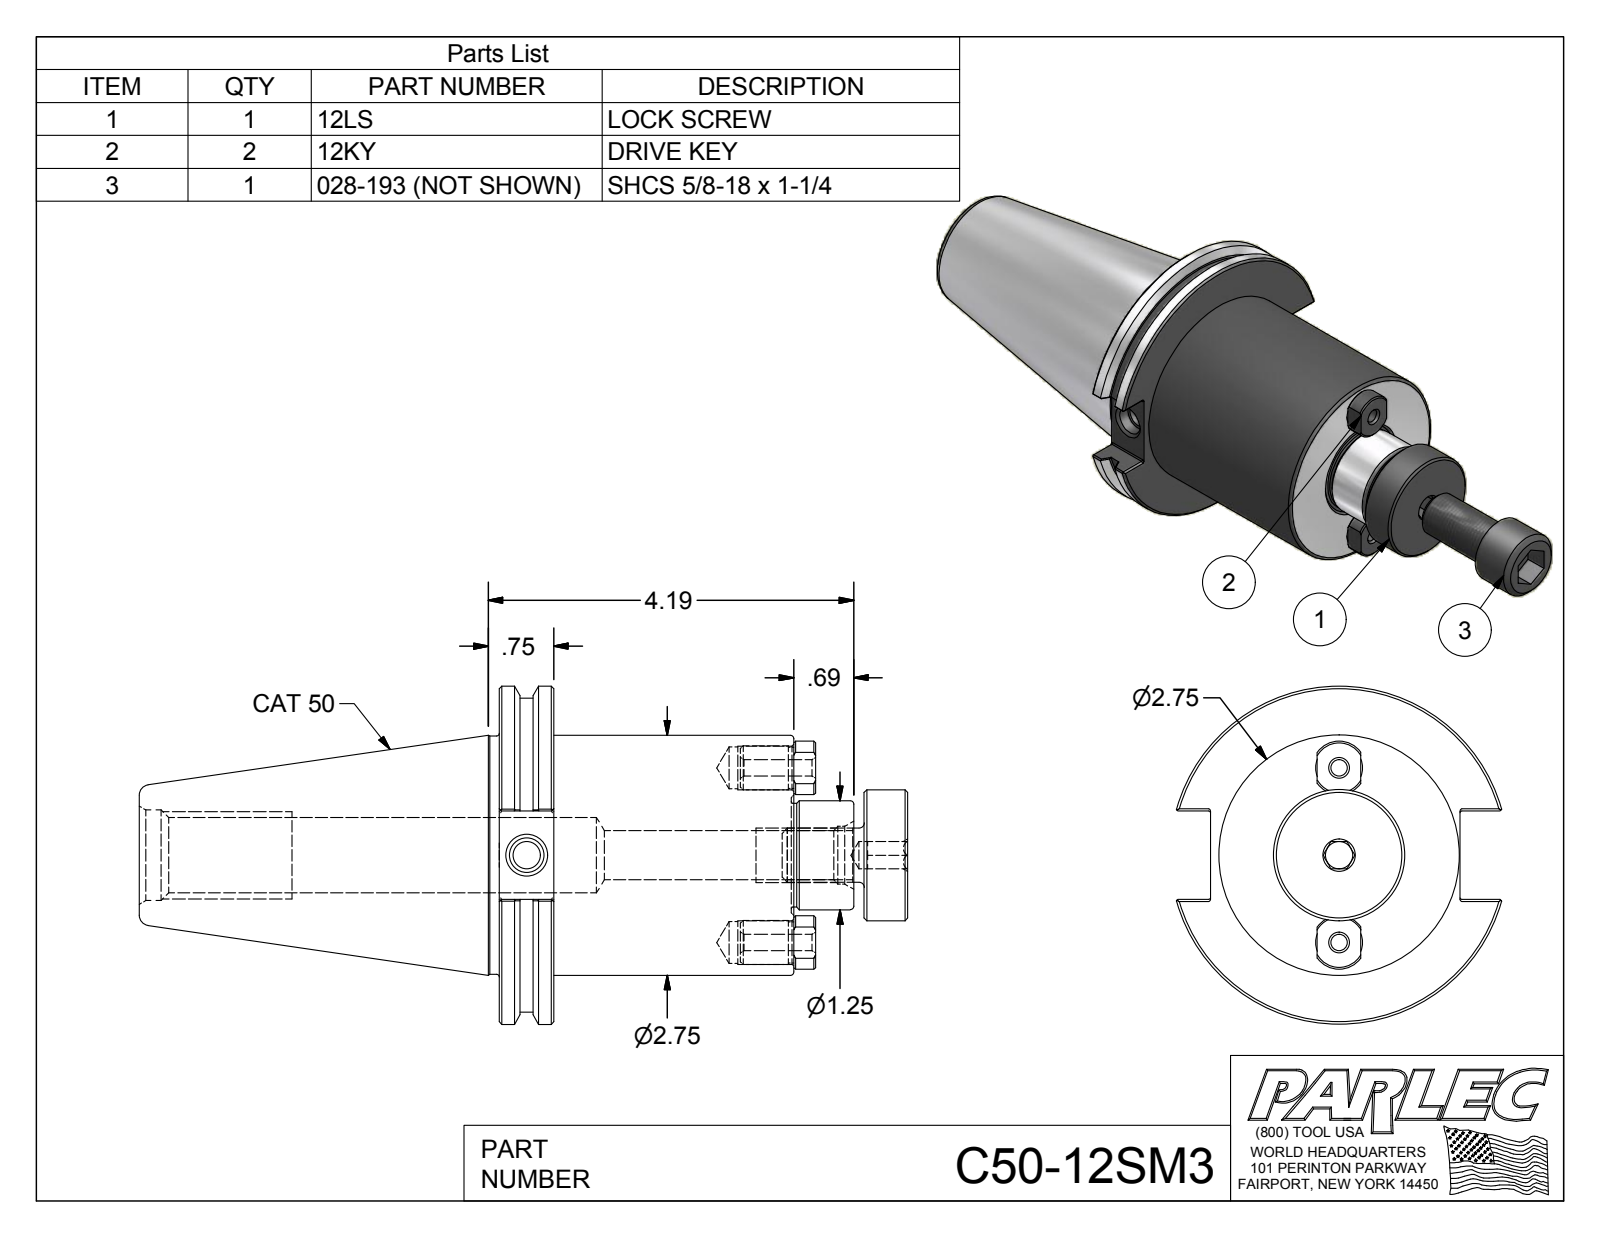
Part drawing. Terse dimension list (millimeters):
name: C50-12SM3; C50-12SM3-1; 12KY; 12LS (+1 more)
written by: Autodesk Inventor 2012 (AUTOMOTIVE_DESIGN)
unit: mm
bodies: 5 solids, 172 faces (67 planar, 47 cylindrical, 58 other)
size: 274.5 × 98.4 × 94.7
volume: 611 600 mm³; area: 79 160 mm²
holes: 2× ⌀4.8, 2× ⌀12.2, 2× ⌀12.7, 1× ⌀7.9, 1× ⌀8, 1× ⌀10.1, 1× ⌀14.4, 1× ⌀16.8, 1× ⌀22, 1× ⌀26.4
bosses: 2× ⌀12.8, 2× ⌀11.9, 1× ⌀98.4, 1× ⌀91.3, 1× ⌀69.9, 1× ⌀69.3, 1× ⌀38.1, 1× ⌀31.8
rounds: 12× R0.5, 2× R7.8
face distances: 15.9, 69.9, 85.7, 118.9, 103, 33.2, 12.7, 106.2, 90.3, 20.5
hole spacings: 25.4, 50.8
